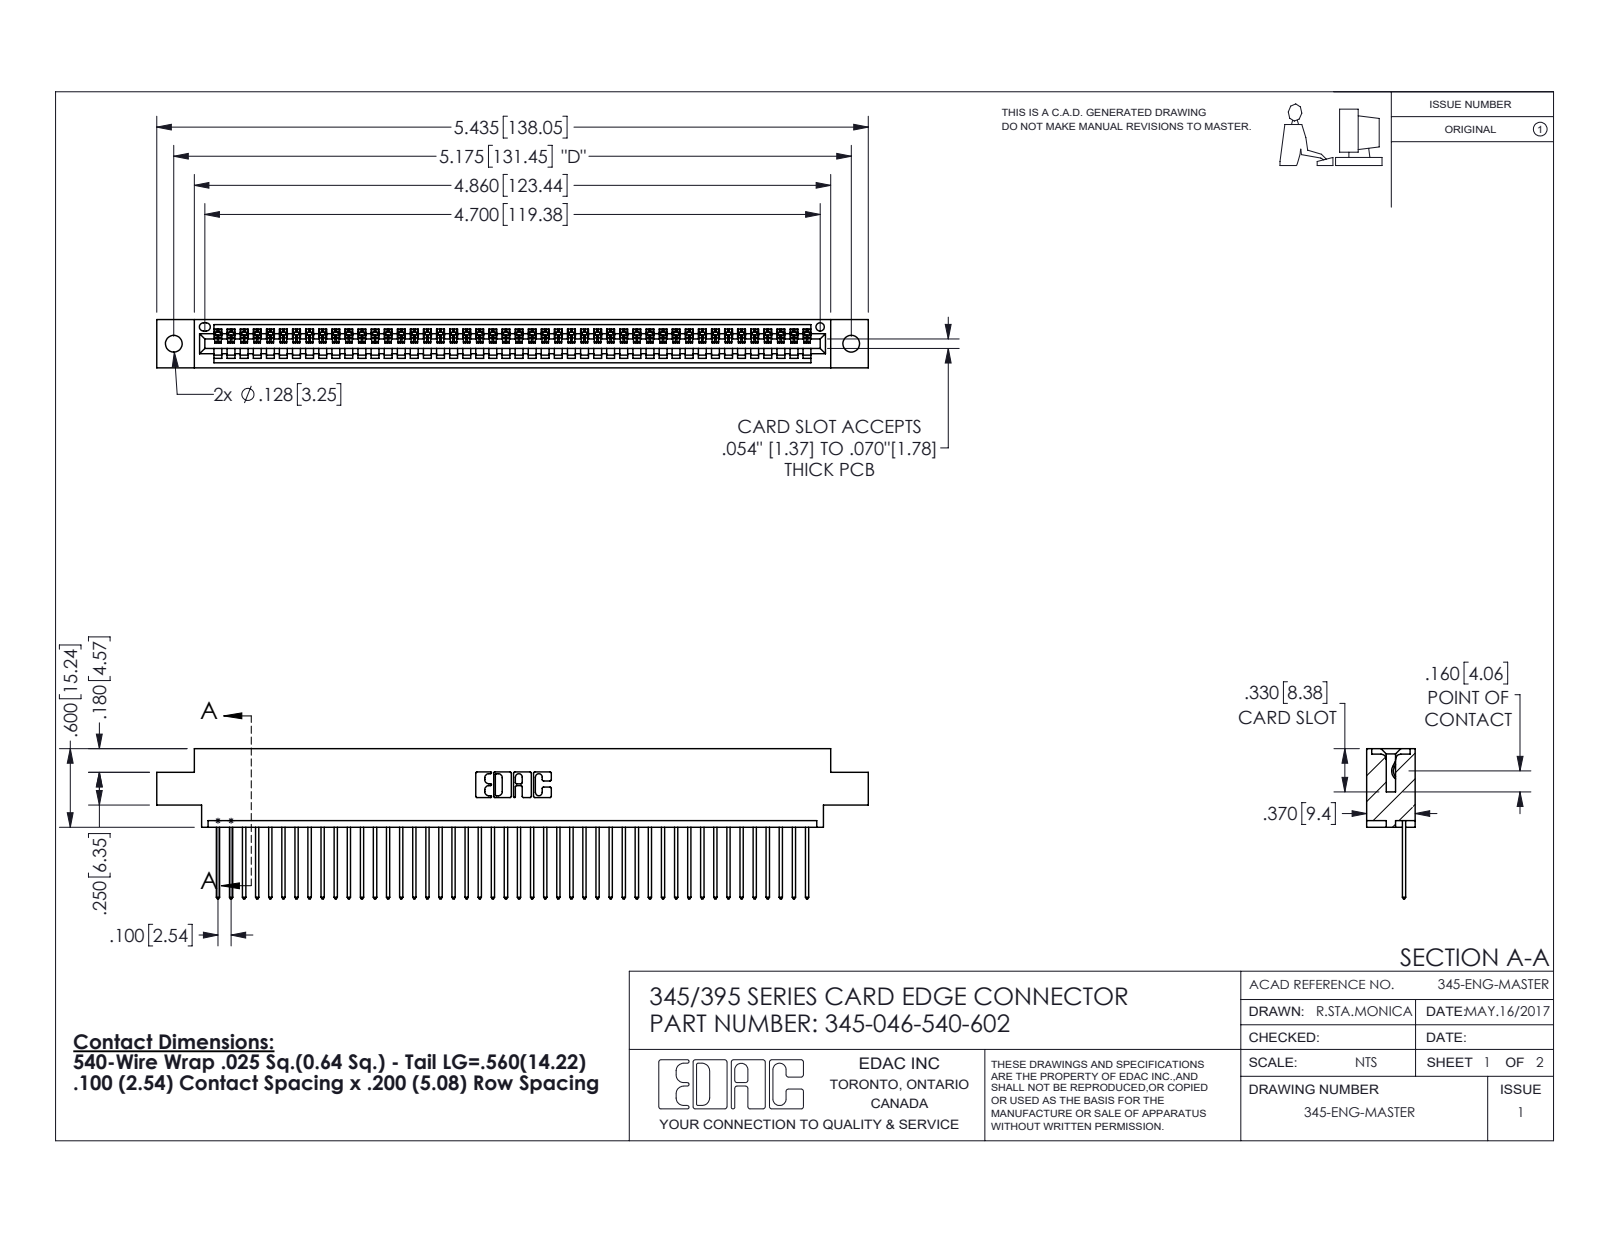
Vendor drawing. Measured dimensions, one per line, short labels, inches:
name: 345 Part_0.170 Offset - 0.128 Dia; 345-292-001_345-293-140; 345-046-540-602
written by: SolidWorks 2016 (CONFIG_CONTROL_DESIGN)
unit: in
bodies: 47 solids, 2798 faces (1924 planar, 874 cylindrical, 0 other)
size: 5.435 × 1.147 × 0.37
volume: 0.797 in³; area: 27.45 in²
holes: 2× ⌀0.128, 1× ⌀0.064
rounds: 92× R0.006, 92× R0.01, 22× R0.01, 6× R0.007, 6× R0.031, 3× R0.026, 2× R0.031, 2× R0.04
face distances: 0.298, 0.072, 0.37, 0.098, 0.272, 0.025, 0.2, 0.225, 0.175, 0.149
hole spacings: 0.27, 4.939, 5.175
